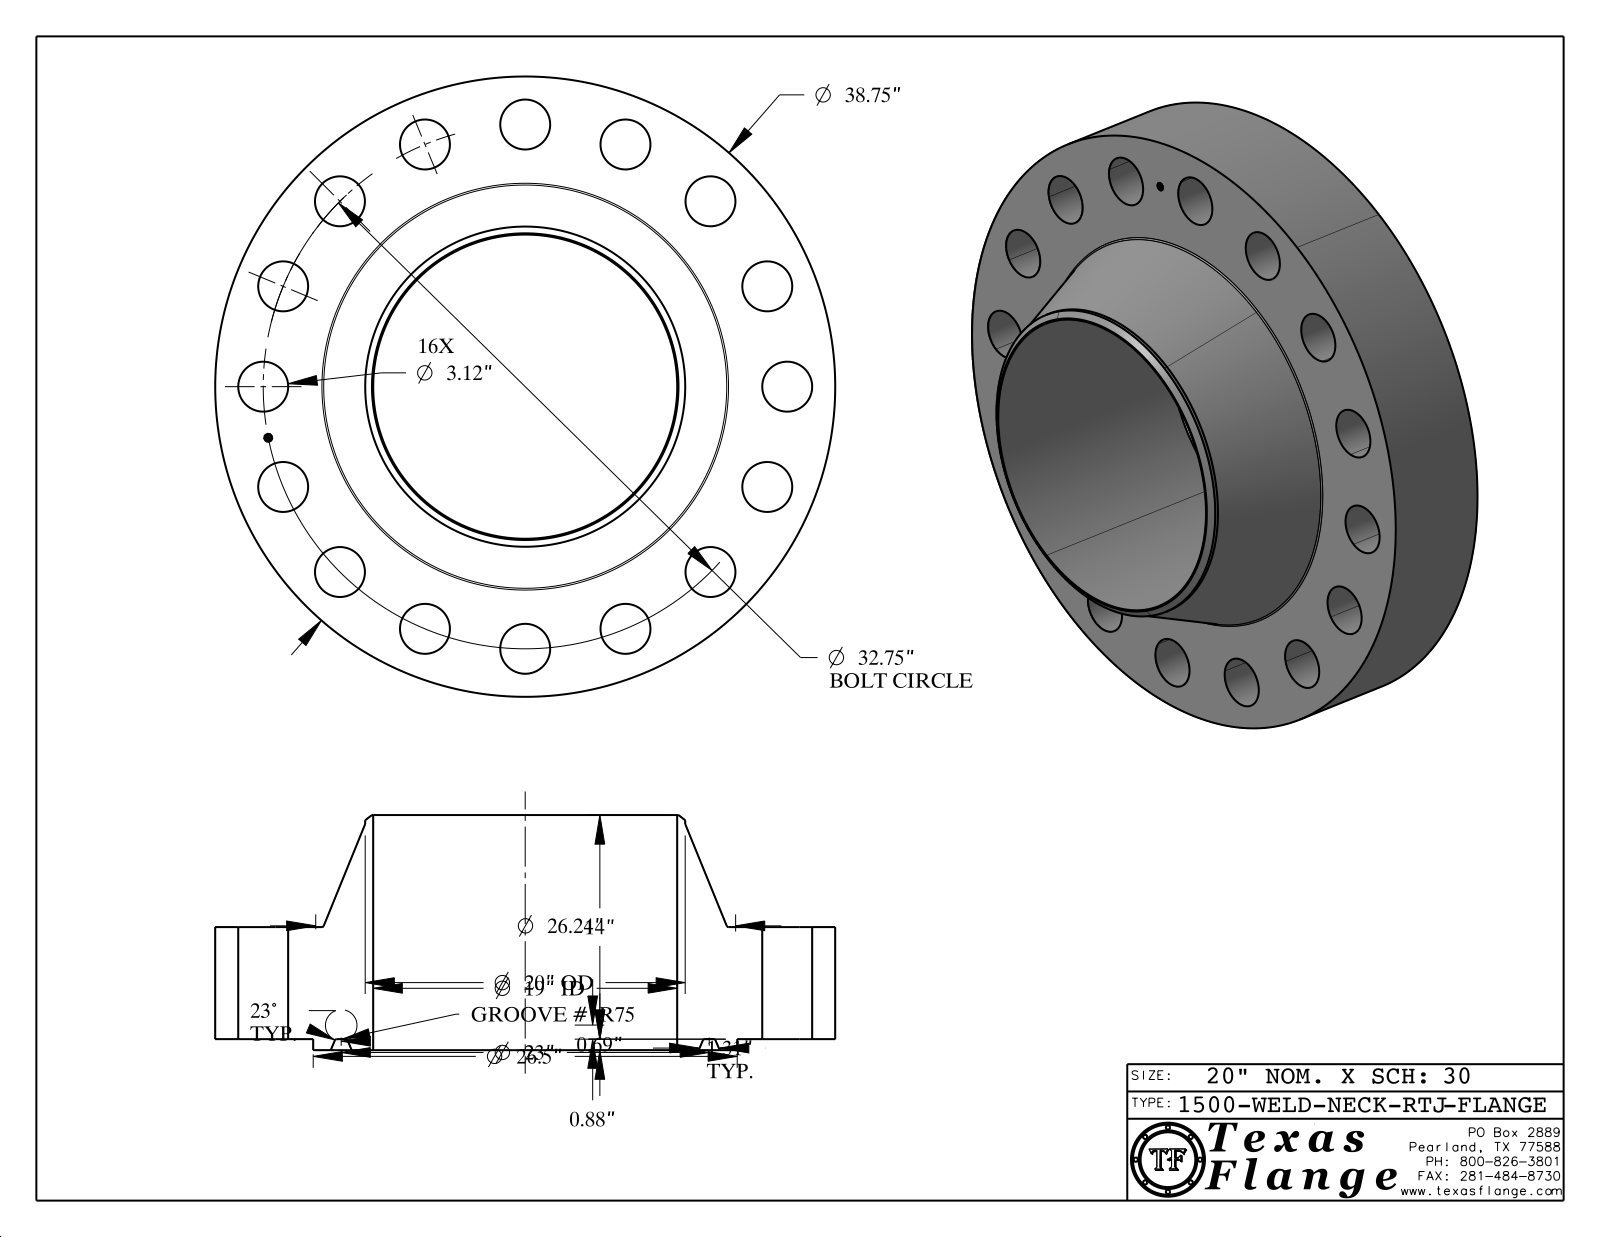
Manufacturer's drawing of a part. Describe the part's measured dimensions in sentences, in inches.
The part is named "1500-WELD-NECK-RTJ". Its 3-D file was written by "CATIA V5 STEP AP214 (AUTOMOTIVE_DESIGN)". It is 1 solid with 445 faces: 371 planar, 60 cylindrical and 14 other. Overall it measures 38.75 by 38.75 by 14.688 inches. Its volume is 6 336 cubic inches and its surface area 4 823 square inches. Round holes: 16 of diameter 3.12, 1 of diameter 0.495, 1 of diameter 19. Round bosses or shafts: 8 of diameter 0.03, 1 of diameter 38.75, 1 of diameter 26.5, 1 of diameter 20, 1 of diameter 0.39. The main face-to-face distances are 7, 0.688, 7.688, 14.688, 14, 7.673, 6.985, 0.015, 7.015, 0.148. The hole center spacings are 18.195, 16.375, 12.533, 23.157, 30.257, 6.389, 6.389, 27.23.
